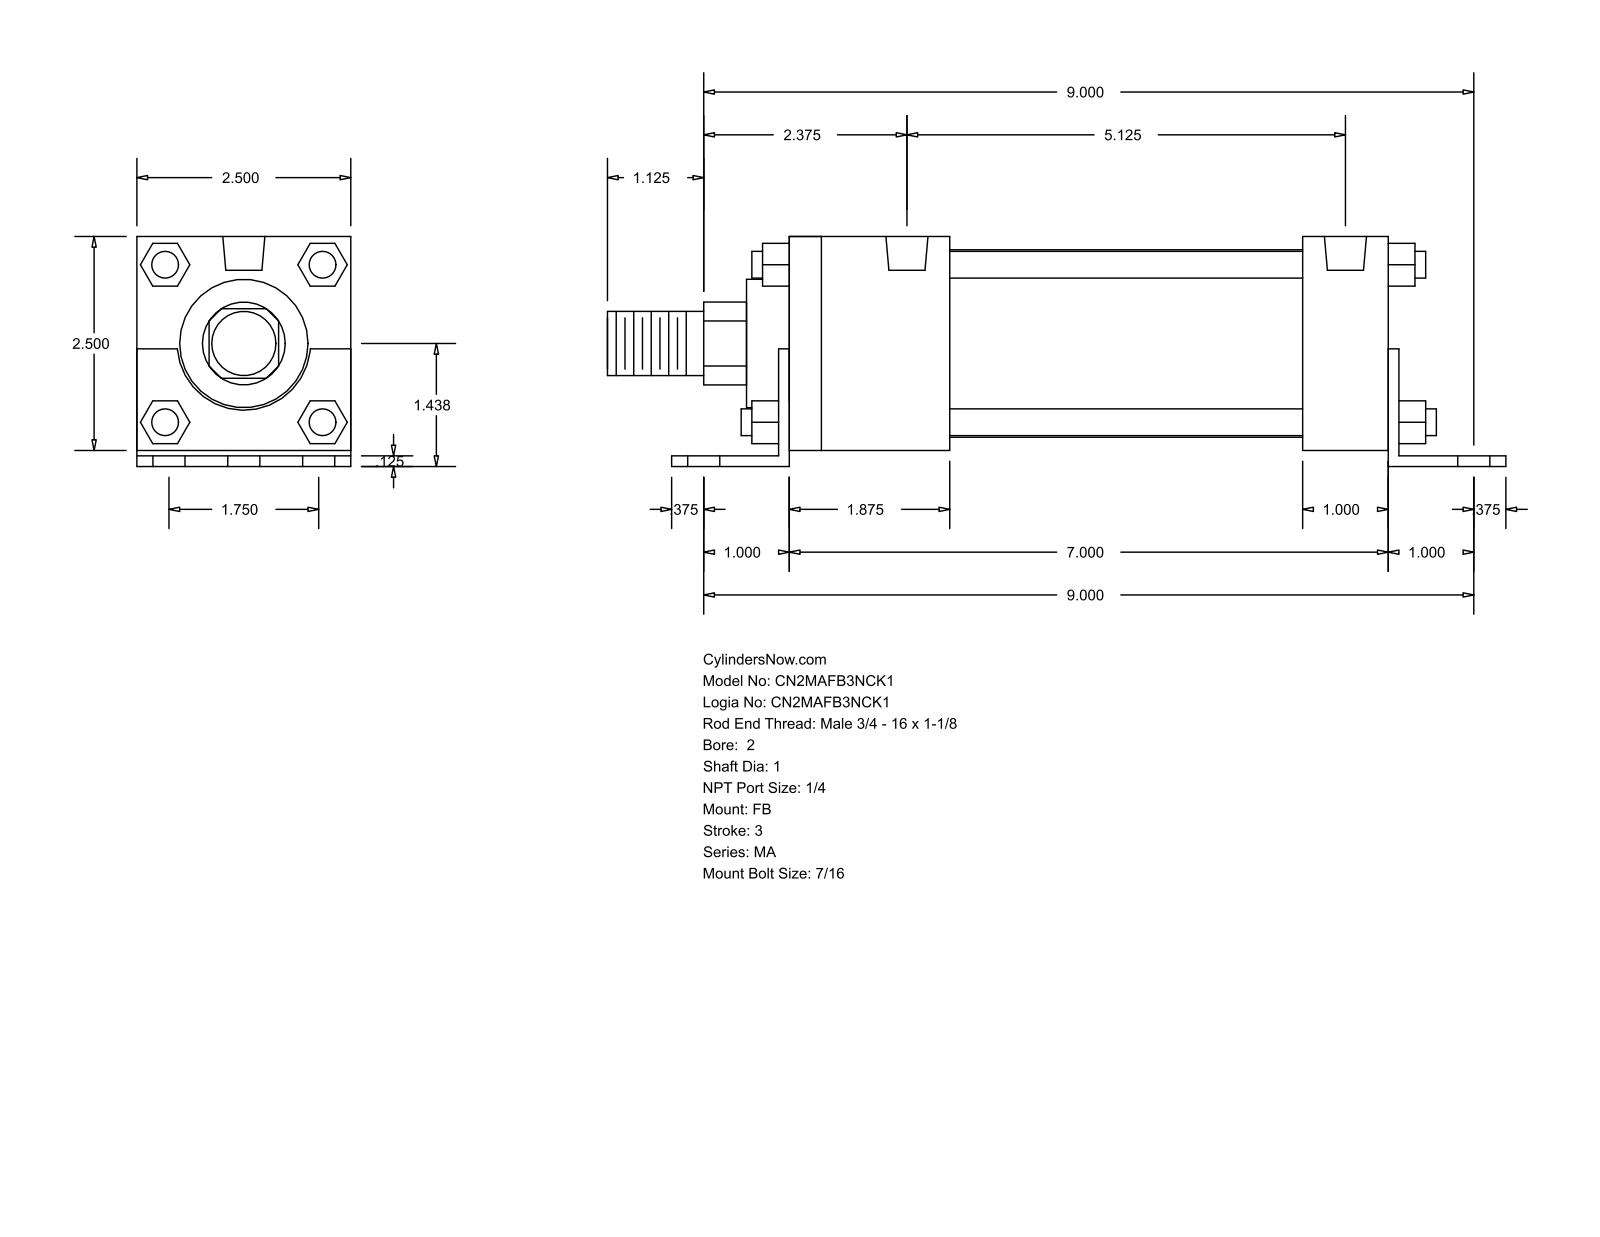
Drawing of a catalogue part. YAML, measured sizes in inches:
part_name: "MA_FB__0200_1"
step_written_by: "GSSL Pune (CONFIG_CONTROL_DESIGN)"
units: inches
bodies: {solids: 0, faces: 140, planar: 105, cylindrical: 35, other: 0}
overall_size: [10.5, 2.687, 2.5]
round_holes:
  - {diameter: 0.437, count: 6}
  - {diameter: 0.313, count: 4}
  - {diameter: 0.492, count: 2}
round_bosses_or_shafts:
  - {diameter: 0.313, count: 4}
  - {diameter: 2.19, count: 1}
  - {diameter: 1.5, count: 1}
  - {diameter: 1, count: 1}
  - {diameter: 0.75, count: 1}
partial_cylinders:
  - {radius: 0.484, count: 1}
  - {radius: 0.78, count: 1}
face_to_face_distances: [2.5, 0.125, 0.187, 2.687, 0.063, 2.563, 0.5, 0.125, 7, 7.125]
hole_center_spacings: [0.875, 9.043, 9, 1.737, 1.75, 2.531, 5.125, 6.682]
